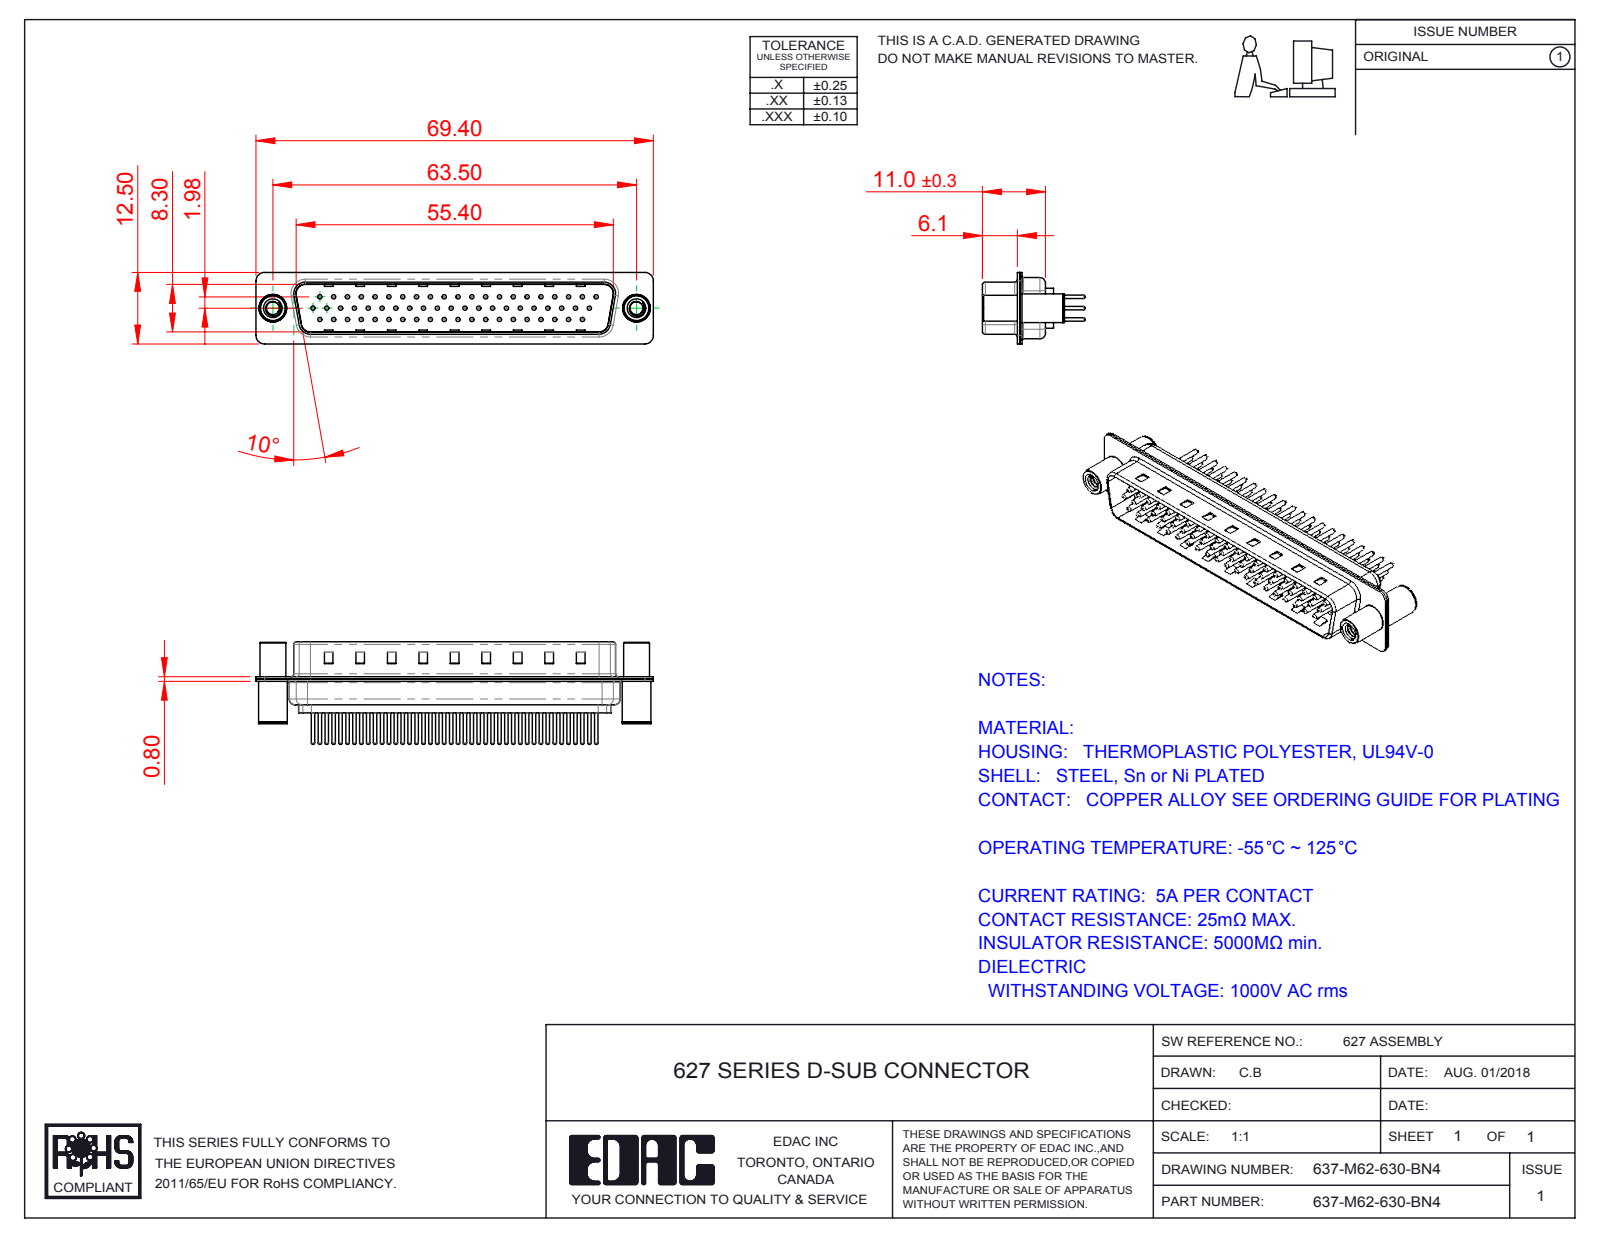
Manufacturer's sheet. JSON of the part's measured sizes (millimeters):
{"part_name": "637-M62-630-BN4; 637M 4-40 Threaded Standoff and Board Spacer; 637M Shell Front_62 Contacts; 637M Shell Rear_62 Contacts (+4 more)", "step_written_by": "SolidWorks 2016 (CONFIG_CONTROL_DESIGN)", "units": "millimeters", "bodies": {"solids": 67, "faces": 2792, "planar": 643, "cylindrical": 1061, "other": 1088}, "overall_size": [69.4, 17.9, 12.5], "volume_mm3": 4205, "surface_area_mm2": 11942, "round_holes": [[0.75, 62], [1.6, 62], [2, 62], [2.26, 2], [3.26, 2], [4, 2], [4.8, 2]], "round_bosses_or_shafts": [[1.5, 62], [0.6, 62], [5, 2], [4.9, 2], [4.5, 2]], "partial_cylinders_radius": [[1.5, 16], [2, 12], [0.5, 8], [1.6, 8], [0.25, 4], [0.6, 4], [0.65, 4], [0.9, 4]], "face_to_face_distances": [0.4, 0.8, 9.5, 9.1, 8.7, 9.9, 0.75, 0.35, 5.9, 1.2], "hole_center_spacings": [7.24, 2.32, 2.41, 4.13, 9.65, 4.83, 14.48, 11.04]}
